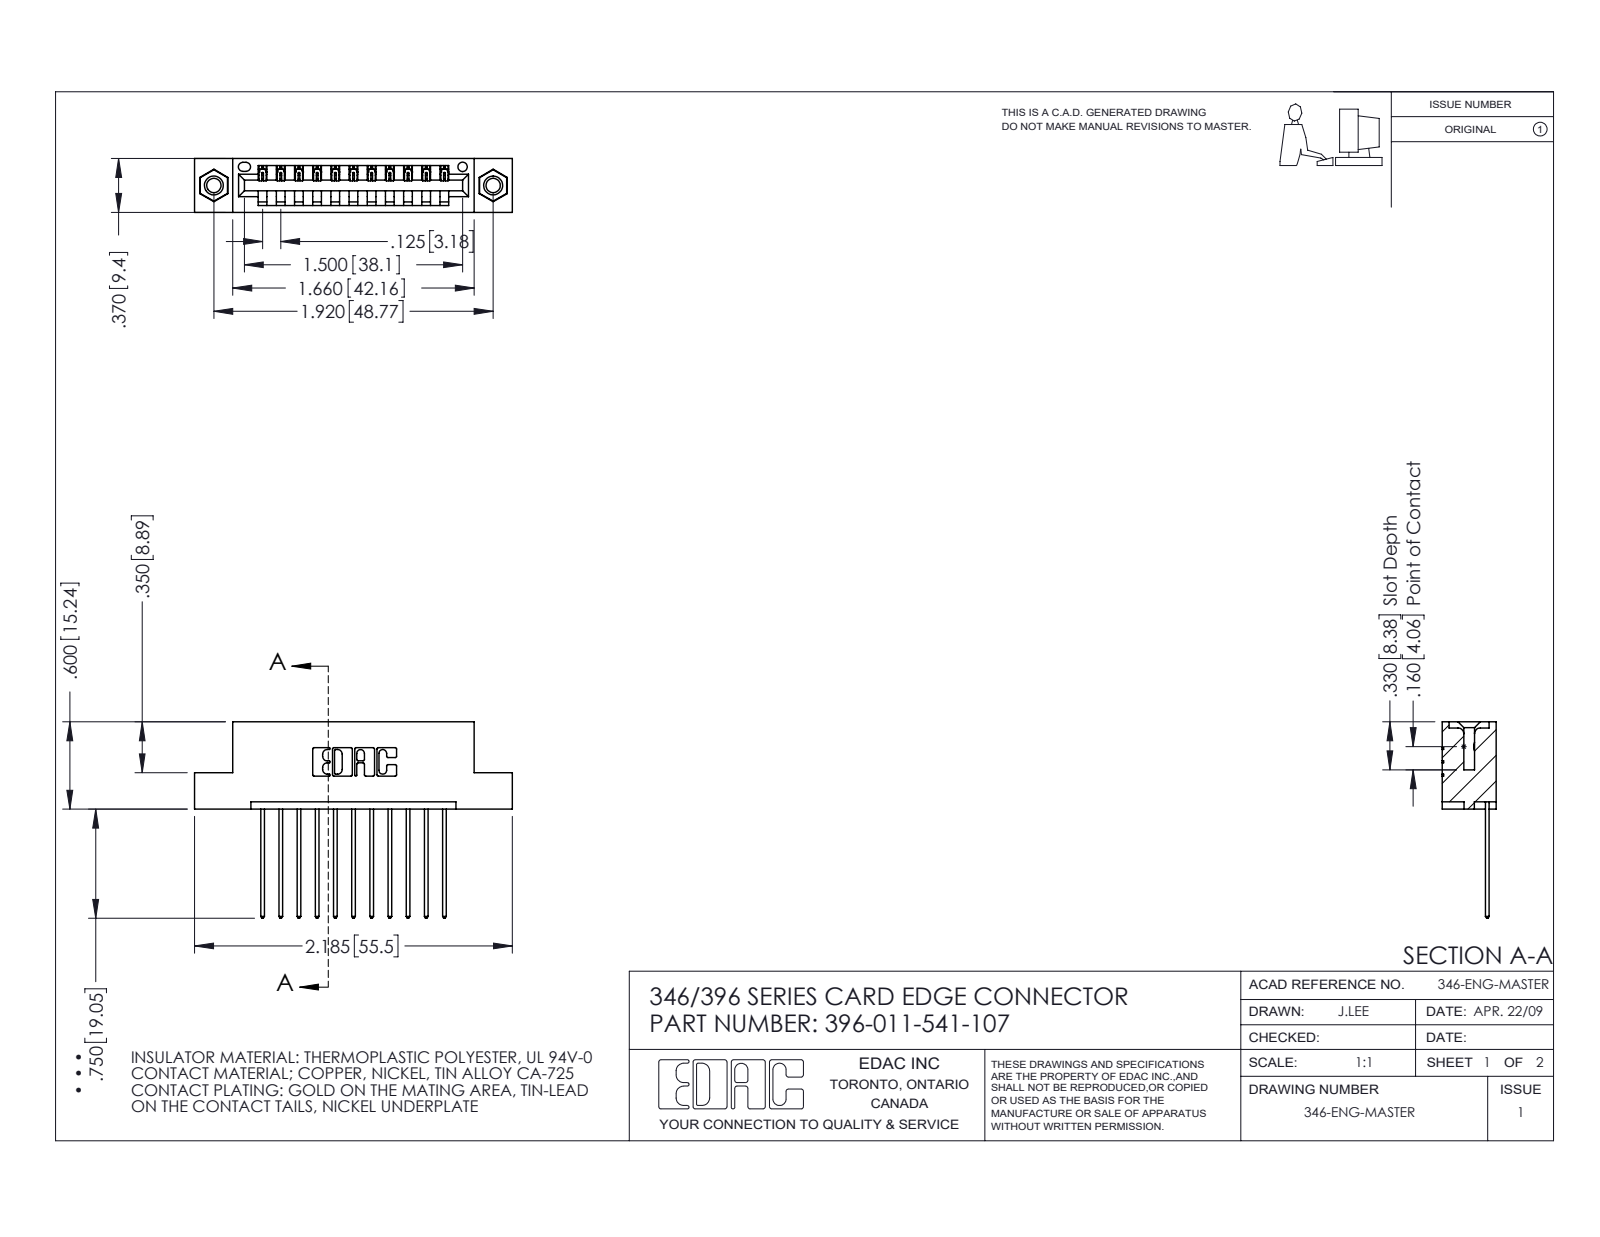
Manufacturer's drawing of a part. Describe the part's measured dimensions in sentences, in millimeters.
The part is named "345-292-001_345-293-141; 396-011-541-107; 345-250-001_345-250-005-103; 346 Part_Flush Mounting Lugs - 0.156 Dia-TI". Its 3-D file was written by "SolidWorks 2016 (CONFIG_CONTROL_DESIGN)". It is 14 solids with 820 faces: 548 planar, 256 cylindrical and 16 other. Overall it measures 55.5 by 34.3 by 9.4 millimeters. Its volume is 5 130 cubic millimeters and its surface area 6 319 square millimeters. Round holes: 2 of diameter 2.5, 2 of diameter 3.2, 2 of diameter 4, 1 of diameter 1.6. Round bosses or shafts: 2 of diameter 3.9. Partial cylindrical surfaces (rounded edges, fillets, slot ends): 22 of radius 0.2, 22 of radius 0.3, 22 of radius 0.3, 6 of radius 0.2, 6 of radius 0.8, 3 of radius 0.7, 2 of radius 0.8, 2 of radius 1. The main face-to-face distances are 6.4, 1.2, 8.2, 9.4, 1.8, 7.6, 0.6, 3.8, 5.6, 2.5. The hole center spacings are 6.2, 43.6, 48.8.
